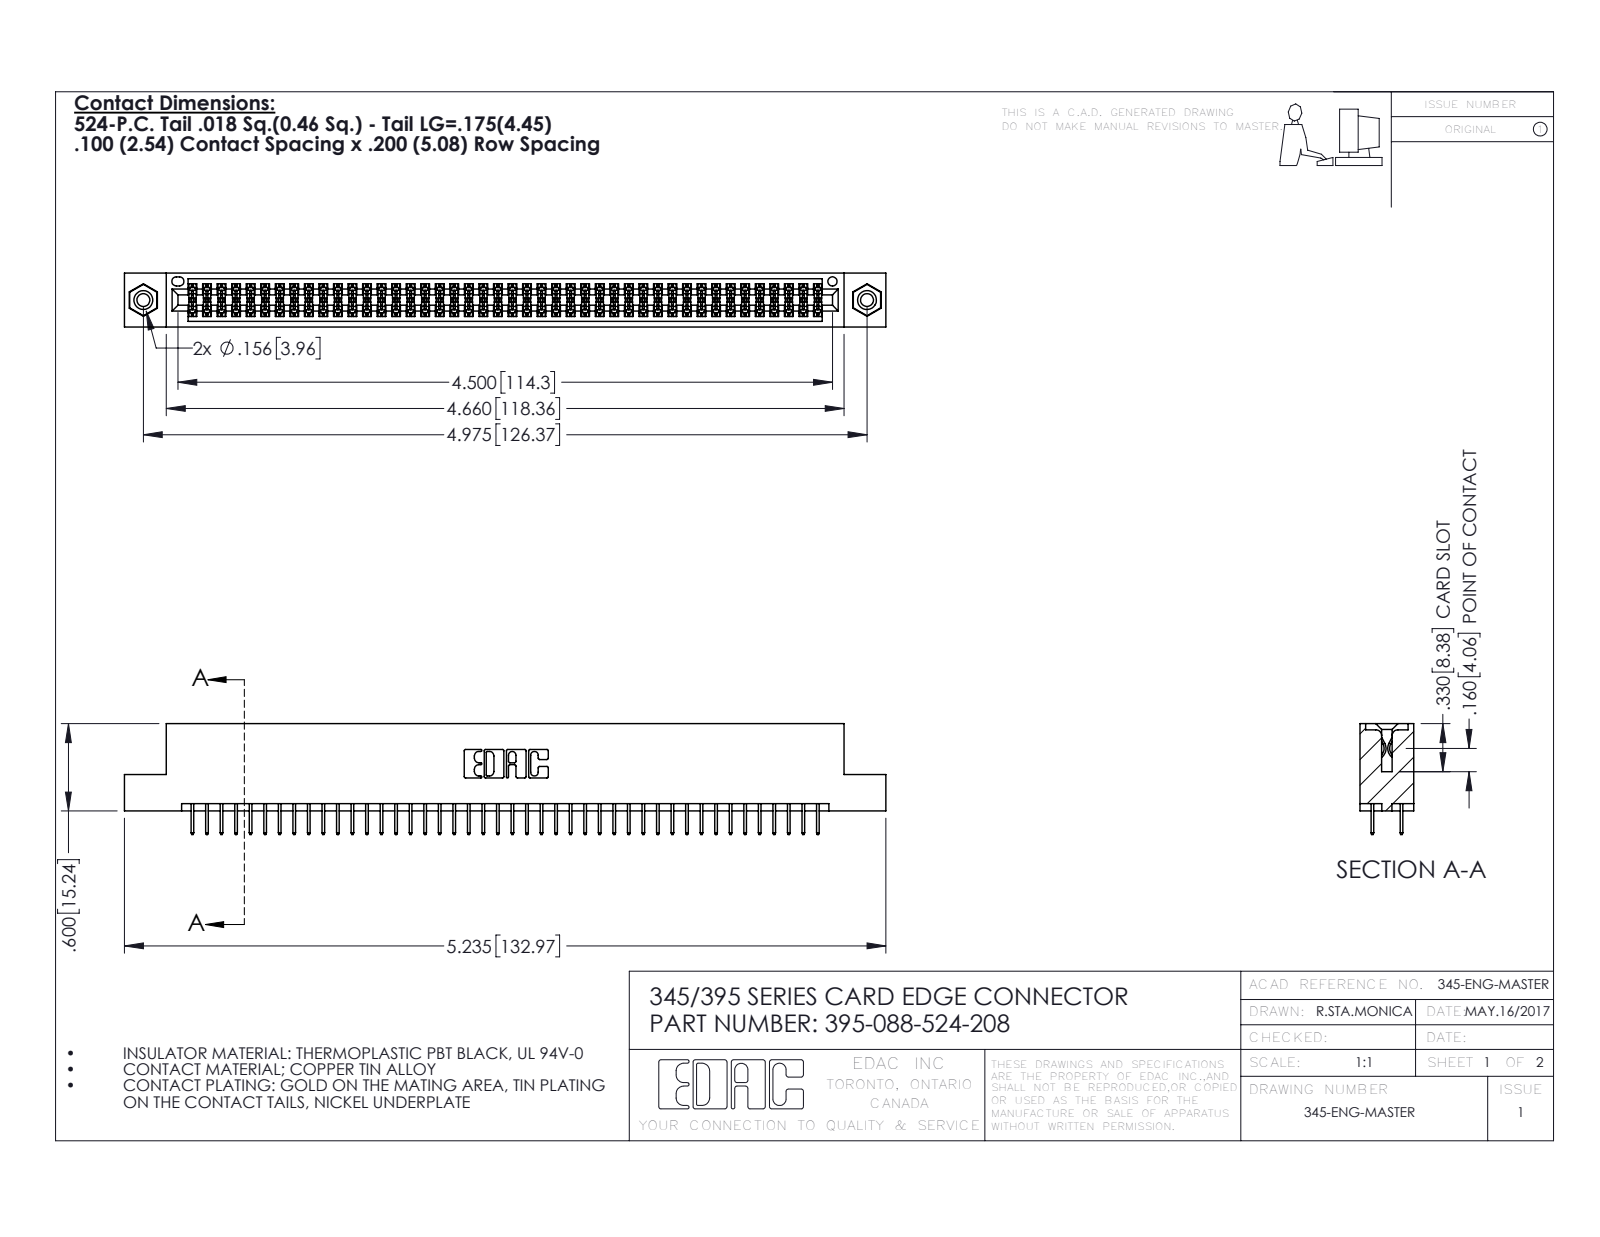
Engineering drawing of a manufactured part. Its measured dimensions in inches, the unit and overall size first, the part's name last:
Units: inches
Overall size (bounding box): 5.235 × 0.762 × 0.37
Round holes (diameter × count): ⌀0.089 ×2, ⌀0.125 ×2, ⌀0.156 ×2, ⌀0.064 ×1
Round bosses / shafts (diameter × count): ⌀0.155 ×2
Partial cylindrical surfaces — rounded edges, fillets, slot ends (radius × count): R0.006 ×132, R0.01 ×22, R0.007 ×6, R0.031 ×6, R0.026 ×3, R0.014 ×2, R0.019 ×2, R0.022 ×2
Main face-to-face distances: 0.072, 0.298, 0.2, 0.37, 0.098, 0.272, 0.025, 0.225, 0.072, 0.175
Hole centre spacings: 0.27, 4.739, 4.975
Volume: 0.781 in³ · Surface area: 28.85 in²
Bodies: 91 solids, 4938 faces (3544 planar, 1378 cylindrical, 16 other)
Part name (STEP PRODUCT): 345 Part_Flush Mounting Lugs - 0.156 Dia-TI; 345-250-001_345-250-003-102; 395-088-524-208; 345-292-001_345-293-124
STEP written by: SolidWorks 2016 (CONFIG_CONTROL_DESIGN)
